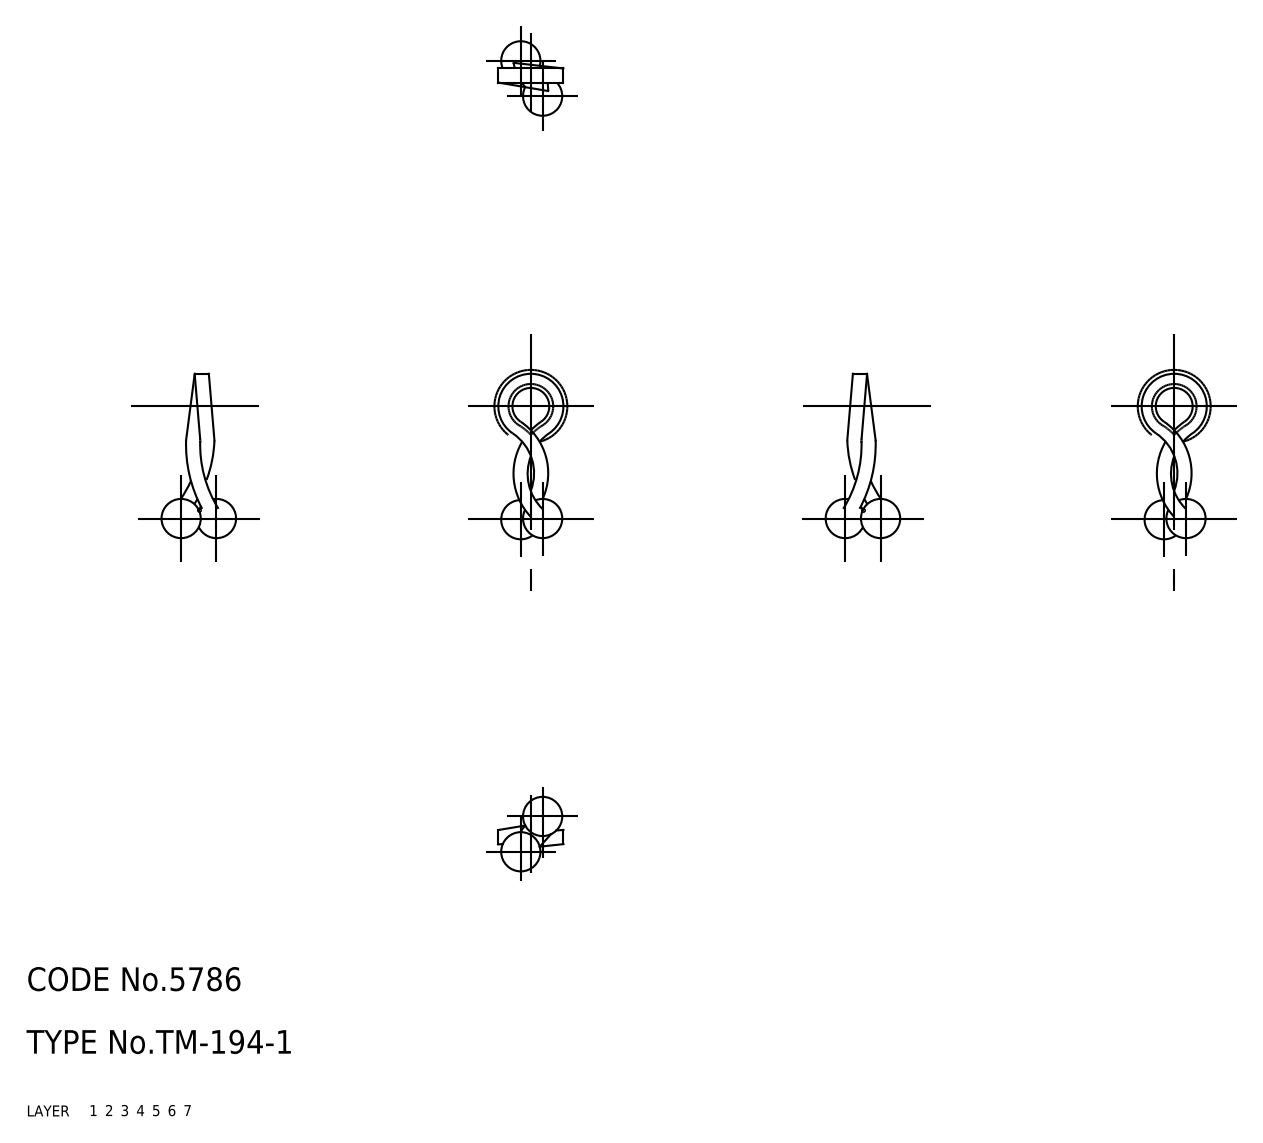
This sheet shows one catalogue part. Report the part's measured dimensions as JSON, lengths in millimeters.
{"part_name": "clip", "step_written_by": "CADfix (AUTOMOTIVE_DESIGN)", "units": "millimeters", "bodies": {"solids": 1, "faces": 24, "planar": 0, "cylindrical": 0, "other": 24}, "overall_size": [20.95, 9.5, 8.56], "volume_mm3": 261, "surface_area_mm2": 441}
